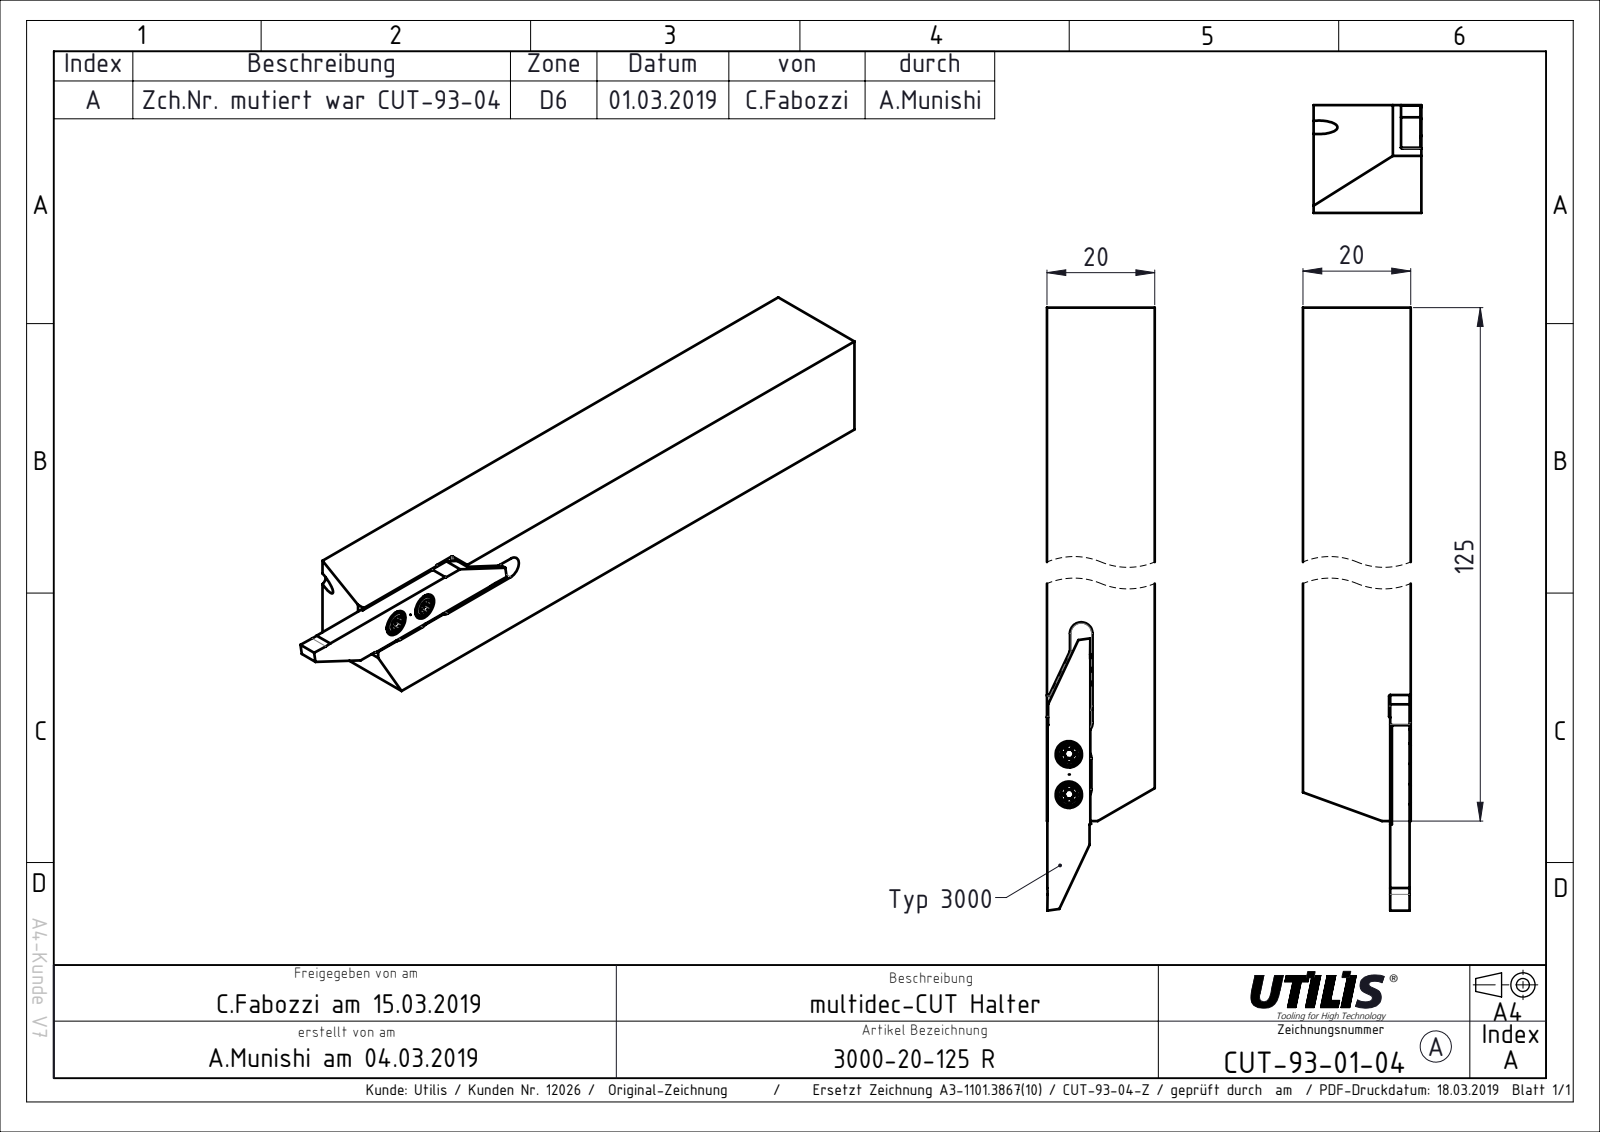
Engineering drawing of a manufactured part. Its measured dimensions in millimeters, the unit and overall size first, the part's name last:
Units: millimetres
Overall size (bounding box): 141.5 × 20 × 20
Round holes (diameter × count): ⌀2.5 ×2, ⌀4.9 ×2
Partial cylindrical surfaces — rounded edges, fillets, slot ends (radius × count): R2.1 ×4, R0.15 ×2, R10 ×2
Main face-to-face distances: 20, 3.8, 16.2, 3.6, 19.8, 12, 8, 11.55, 0.45, 8.45
Hole centre spacings: 3.75, 7.5
Volume: 48 752 mm³ · Surface area: 11 908 mm²
Bodies: 2 solids, 55 faces (36 planar, 19 cylindrical, 0 other)
Part name (STEP PRODUCT): CUT-93-Kunde_04; CUT-Vorlage 3000 R+L Lang Kunde; CUT-93-Kunde; CUT-93-04 (+1 more)
STEP written by: SolidWorks 2015 (CONFIG_CONTROL_DESIGN)
